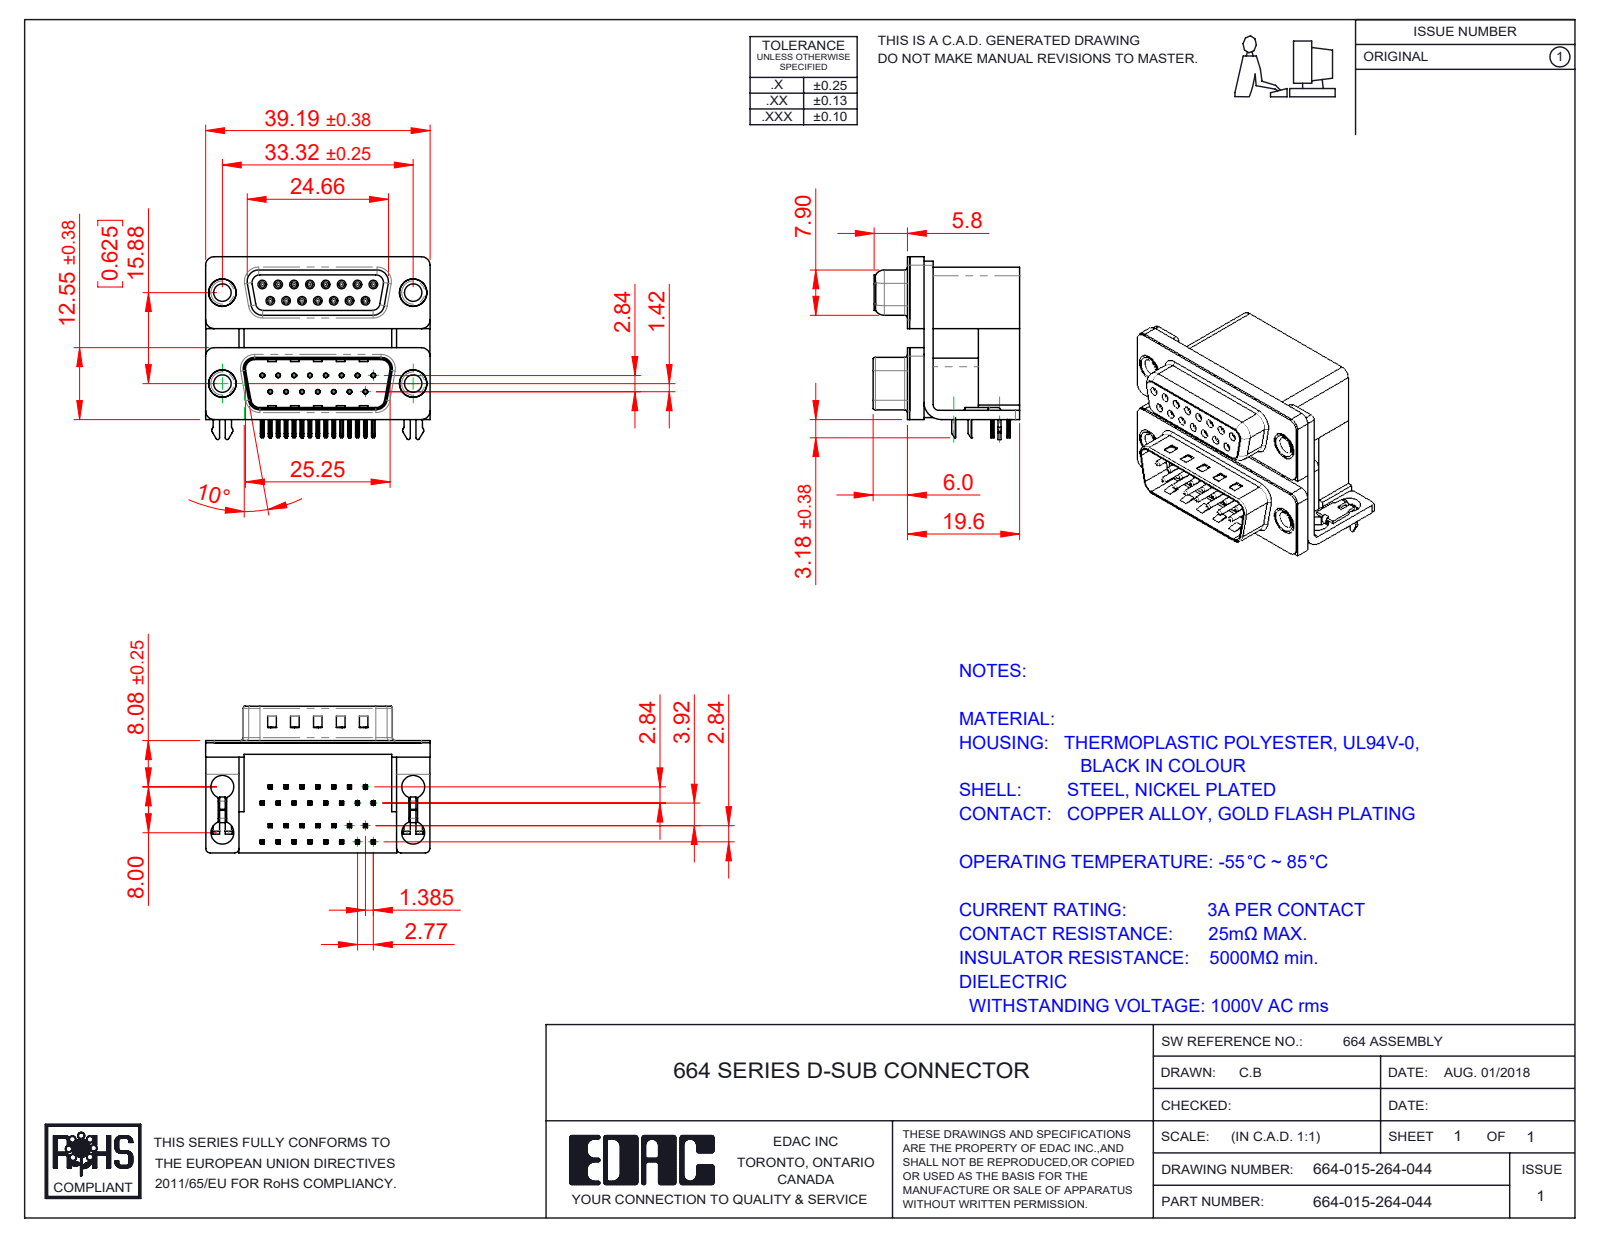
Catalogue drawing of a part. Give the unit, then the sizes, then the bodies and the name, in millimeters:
Units: millimetres
Overall size (bounding box): 39.19 × 31.93 × 25.6
Round holes (diameter × count): ⌀0.8 ×30, ⌀0.35 ×15, ⌀0.9 ×15, ⌀4 ×8, ⌀3.05 ×4, ⌀3.5 ×4, ⌀4.8 ×4, ⌀5 ×4
Round bosses / shafts (diameter × count): ⌀1.2 ×15, ⌀0.75 ×15, ⌀4.9 ×4, ⌀4.75 ×4, ⌀3.85 ×4
Partial cylindrical surfaces — rounded edges, fillets, slot ends (radius × count): R0.1 ×121, R0.25 ×66, R0.15 ×60, R0.12 ×30, R0.35 ×30, R0.5 ×16, R1.5 ×16, R0.34 ×15
Main face-to-face distances: 0.4, 19.2, 16.7, 2.5, 7.2, 12, 9.5, 2.19, 10.7, 2.9
Hole centre spacings: 3.16, 2.77, 16.12, 5.54, 16.82, 8.31, 15.88, 17.92
Volume: 14 500 mm³ · Surface area: 16 367 mm²
Bodies: 43 solids, 3936 faces (2093 planar, 1008 cylindrical, 835 other)
Part name (STEP PRODUCT): 664 2 Prong Board Lock_4; 664 Mounting Bracket_2ProngL; 664 Shell Receptacle_15 Contacts; 664 Housing Upper_15 Contacts L (+8 more)
STEP written by: SolidWorks 2020 (CONFIG_CONTROL_DESIGN)
